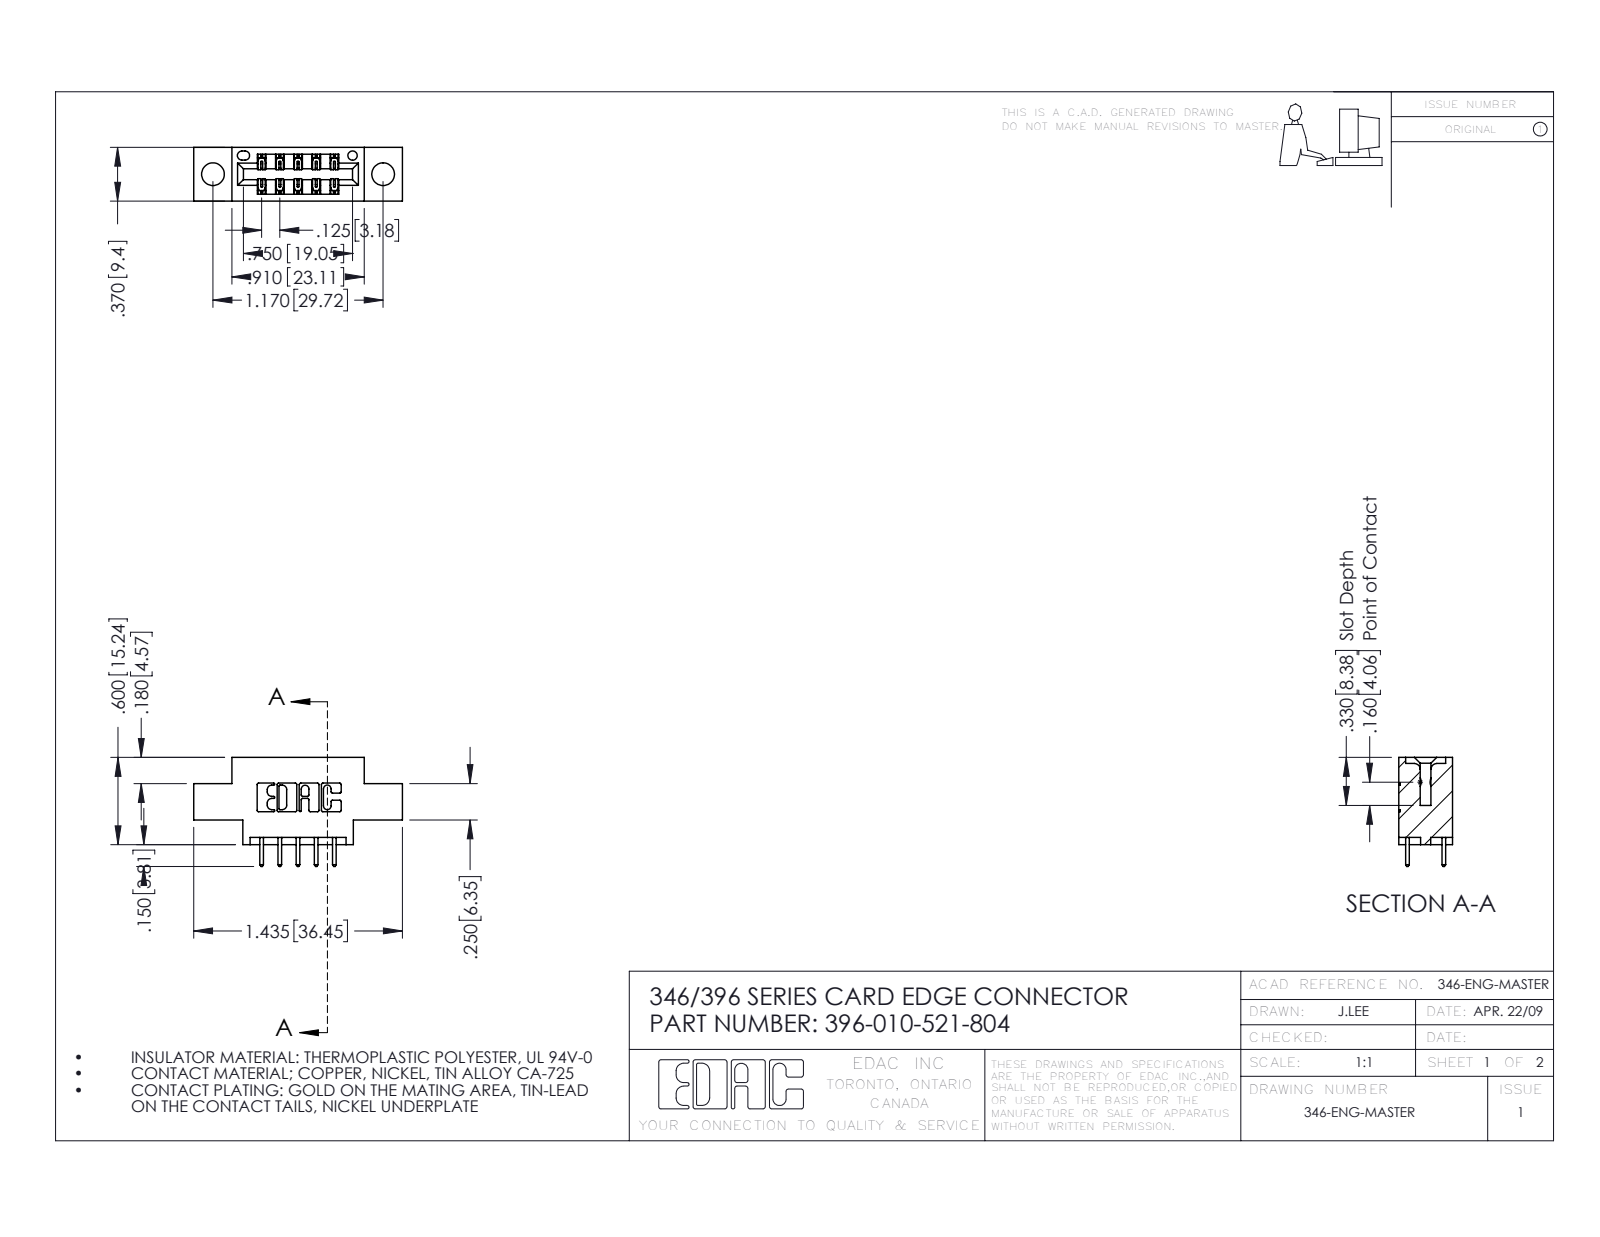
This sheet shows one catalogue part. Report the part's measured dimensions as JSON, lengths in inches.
{"part_name": "346 Part_0.170 Offset - 0.156 Dia-TH; 345-292-001_345-293-121; 396-010-521-804", "step_written_by": "SolidWorks 2016 (CONFIG_CONTROL_DESIGN)", "units": "inches", "bodies": {"solids": 11, "faces": 646, "planar": 430, "cylindrical": 216, "other": 0}, "overall_size": [1.435, 0.75, 0.37], "volume_in3": 0.184, "surface_area_in2": 5.48, "round_holes": [[0.156, 2], [0.064, 1]], "partial_cylinders_radius": [[0.01, 22], [0.006, 15], [0.01, 10], [0.007, 6], [0.031, 6], [0.026, 3], [0.014, 2], [0.022, 2]], "face_to_face_distances": [0.25, 0.37, 0.048, 0.322, 0.072, 0.298, 0.025, 0.148, 0.222, 0.1], "hole_center_spacings": [0.246, 0.969, 1.17]}
